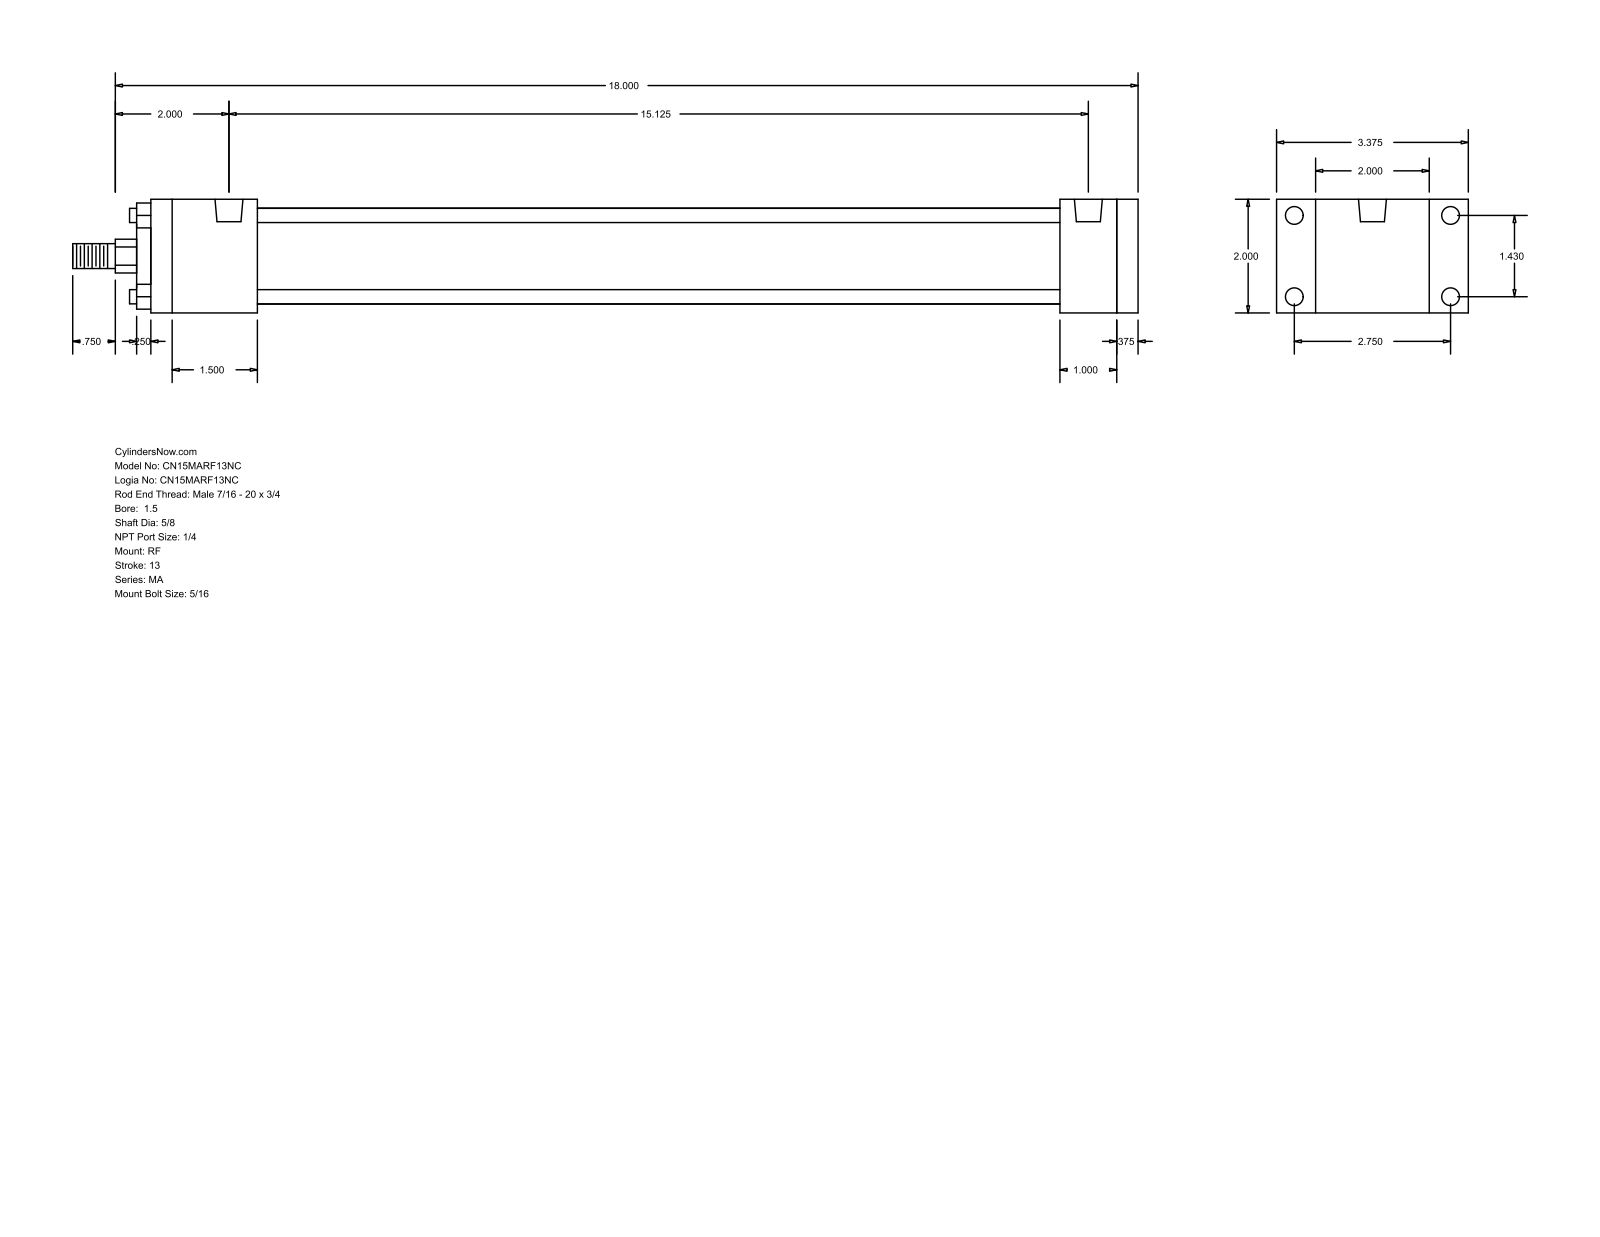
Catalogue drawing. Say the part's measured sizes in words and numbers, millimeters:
The part is named "MA_RF__0150_0.625". Its 3-D file was written by "GSSL Pune (CONFIG_CONTROL_DESIGN)". It is 0 solids with 92 faces: 64 planar, 28 cylindrical and 0 other. Overall it measures 476.25 by 85.72 by 50.8 millimeters. Round holes: 8 of diameter 7.94, 2 of diameter 12.49. Round bosses or shafts: 4 of diameter 6.35, 1 of diameter 42.93, 1 of diameter 28.57, 1 of diameter 15.88, 1 of diameter 11.11. Partial cylindrical surfaces (rounded edges, fillets, slot ends): 1 of radius 7.54. The main face-to-face distances are 50.8, 441.32, 9.52, 431.8, 34.93, 406.39, 25.41, 47.62, 358.77, 384.18. The hole center spacings are 36.32, 69.84, 78.72, 384.18.
